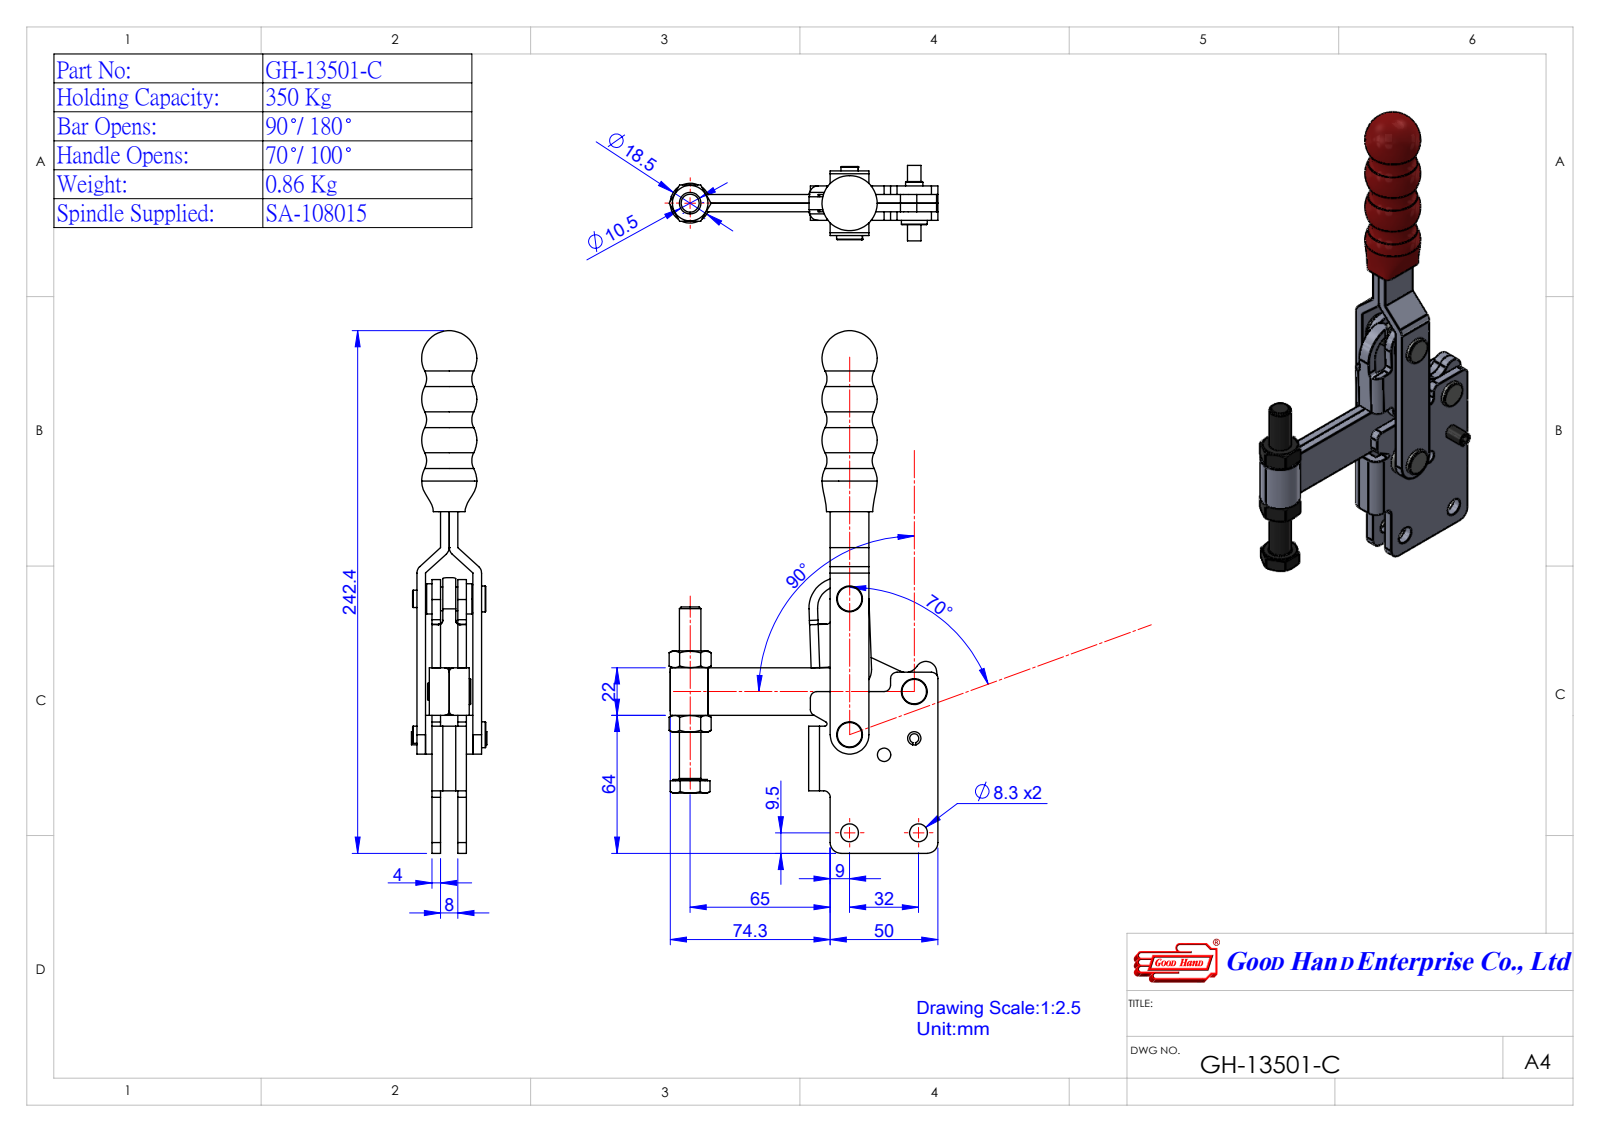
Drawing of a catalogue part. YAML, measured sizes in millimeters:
part_name: "Group4^GH-13501-B(簡化)-1; GH-SA-108015-1^GH-13501-C(簡化)-1; Group2^GH-13501-C(簡化)-1; Group1^GH-13501-C(簡化)-1 (+2 more)"
step_written_by: "SolidWorks 2016 (AUTOMOTIVE_DESIGN)"
units: millimeters
bodies: {solids: 4, faces: 304, planar: 103, cylindrical: 125, other: 76}
overall_size: [242.4, 124.81, 35]
volume: 134740
surface_area: 60990
round_holes:
  - {diameter: 6, count: 5}
  - {diameter: 8.4, count: 2}
  - {diameter: 8.5, count: 1}
  - {diameter: 10, count: 1}
round_bosses_or_shafts:
  - {diameter: 12, count: 4}
  - {diameter: 18.5, count: 1}
  - {diameter: 6.2, count: 1}
partial_cylinders:
  - {radius: 3, count: 5}
  - {radius: 5, count: 5}
  - {radius: 9, count: 5}
  - {radius: 4.1, count: 4}
  - {radius: 1, count: 2}
  - {radius: 2, count: 2}
  - {radius: 0.1, count: 1}
  - {radius: 6, count: 1}
face_to_face_distances: [4, 8, 12, 11, 7, 15, 19, 16, 26, 23]
hole_center_spacings: [39.56, 18.52, 30.04, 30.54, 32, 32.49, 33, 36.06]
